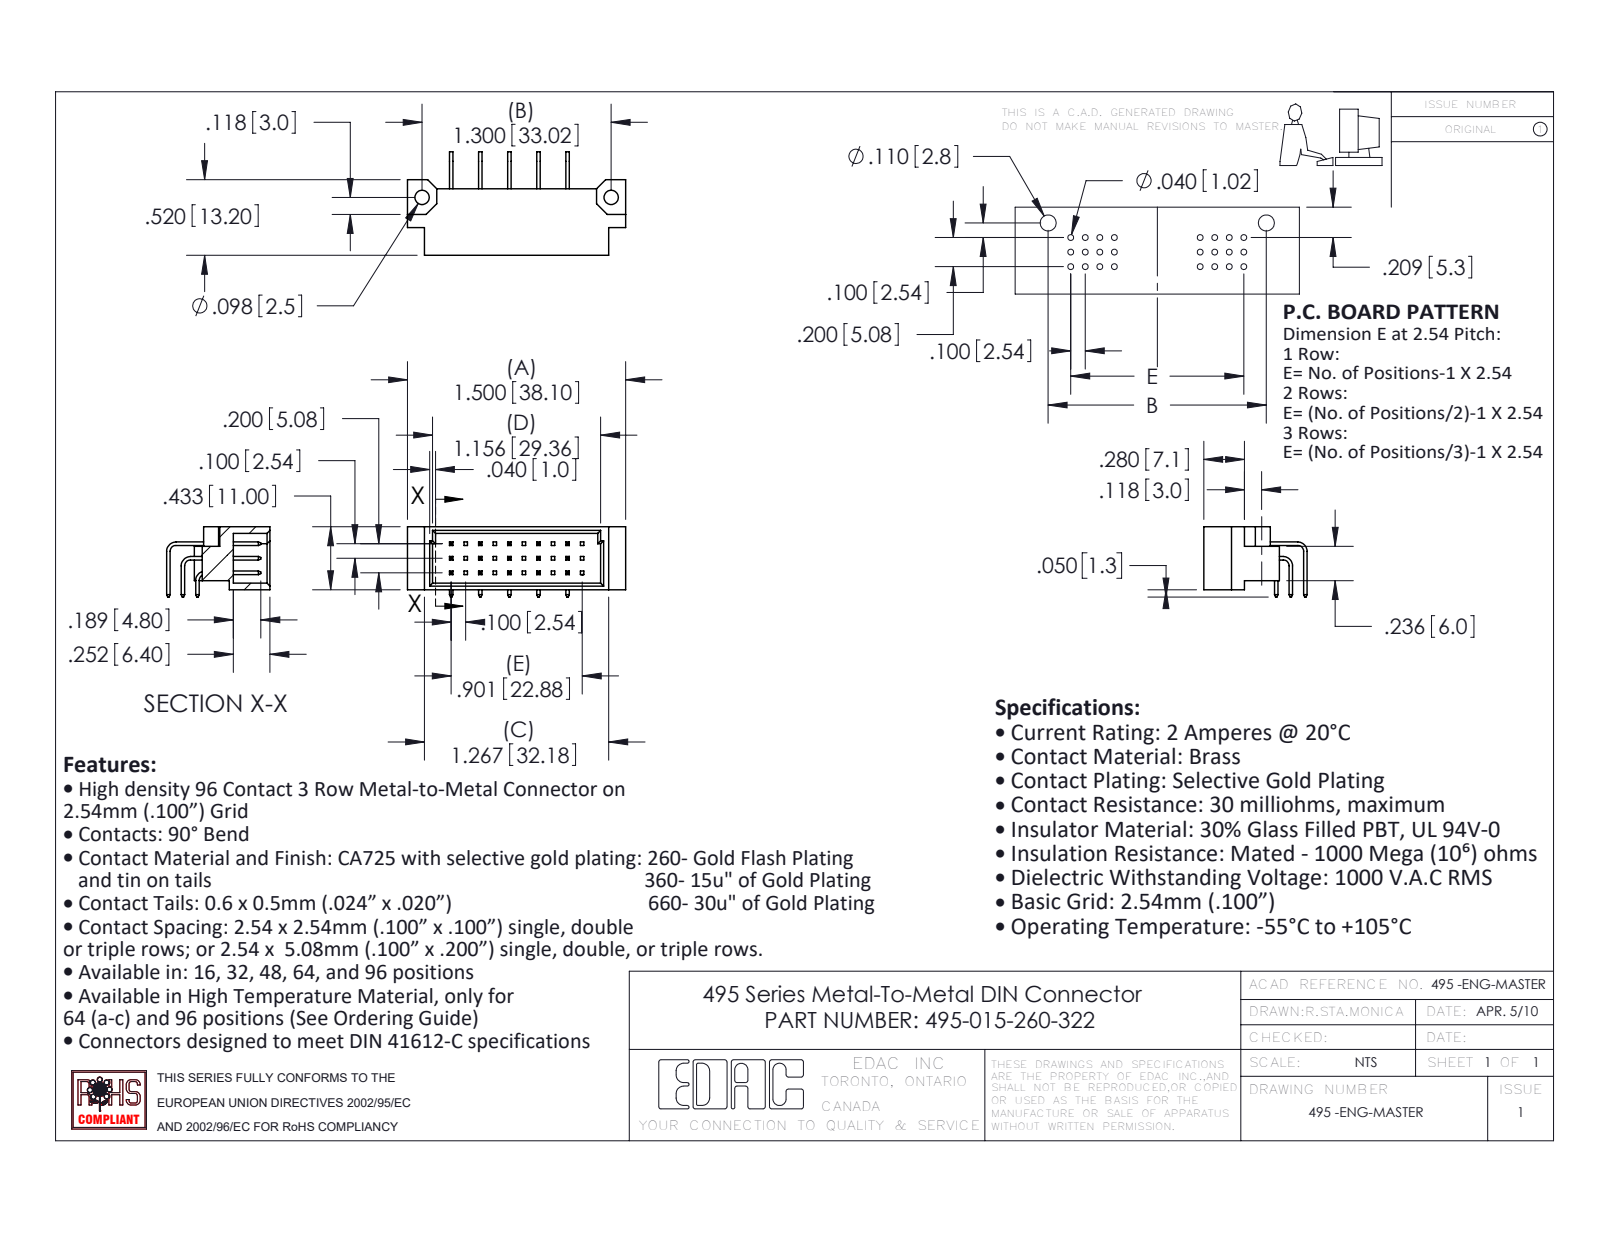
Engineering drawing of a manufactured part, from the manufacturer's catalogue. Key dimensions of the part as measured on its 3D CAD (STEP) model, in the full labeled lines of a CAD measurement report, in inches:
Part name (STEP PRODUCT): 495-290-1; 495-015-260-322; 495 Part_30; 495-290-2 (+1 more)
STEP written by: SolidWorks 2020 (AUTOMOTIVE_DESIGN)
Units: inches
Bodies: 16 solids, 439 faces (405 planar, 34 cylindrical, 0 other)
Overall size (bounding box): 1.5 × 0.711 × 0.483
Volume: 0.157 in³ · Surface area: 5.532 in²
Round holes (diameter × count): ⌀0.098 ×2
Partial cylindrical surfaces — rounded edges, fillets, slot ends (radius × count): R0.04 ×3, R0.065 ×3
Main face-to-face distances: 0.2, 0.388, 0.045, 0.1, 0.205, 0.4, 0.024, 0.433, 0.024, 0.063
Hole centre spacings: 1.3
